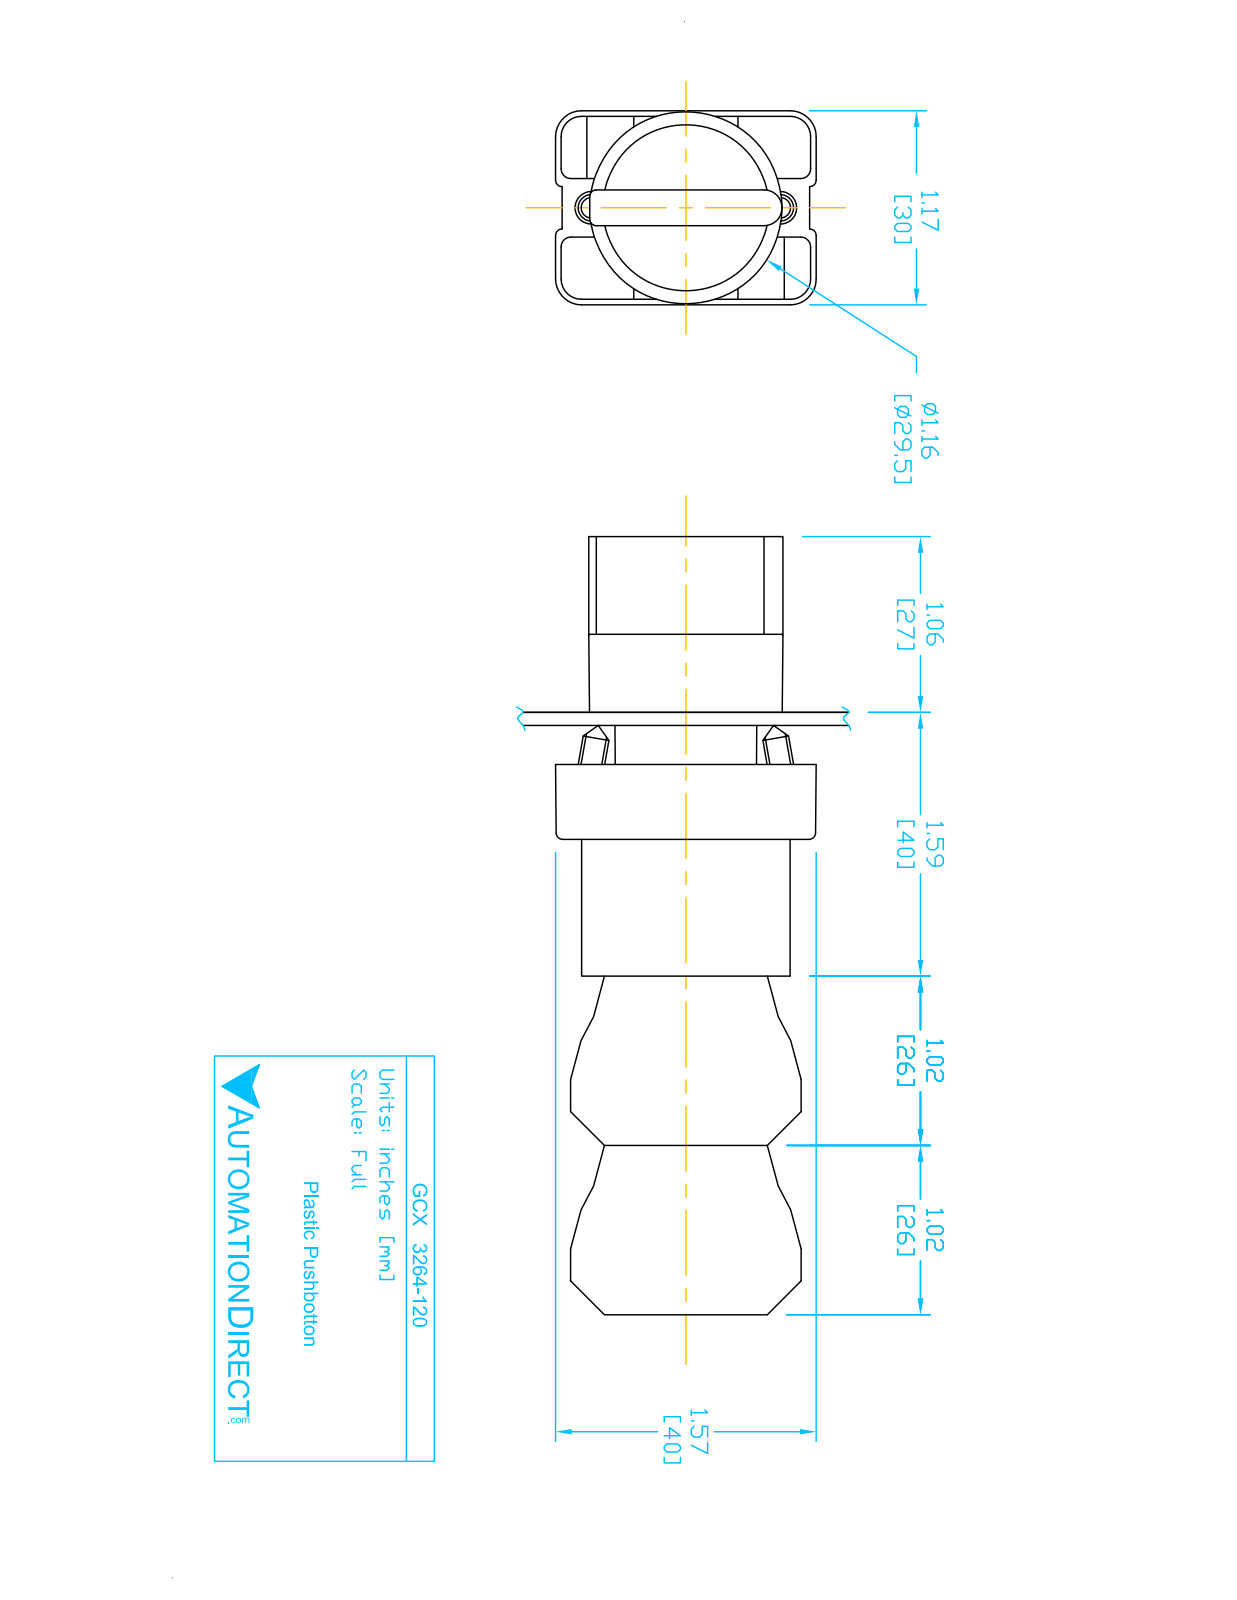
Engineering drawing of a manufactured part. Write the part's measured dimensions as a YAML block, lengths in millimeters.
part_name: "GCX3264 OPERATOR; ecx1030; ecx1040; ECX1050 (+2 more)"
step_written_by: "SolidWorks 2016 (AUTOMOTIVE_DESIGN)"
units: millimeters
bodies: {solids: 11, faces: 724, planar: 488, cylindrical: 193, other: 43}
overall_size: [118.8, 40.2, 29.9]
volume: 77850
surface_area: 38210
round_holes:
  - {diameter: 2, count: 4}
  - {diameter: 2.2, count: 2}
  - {diameter: 3.1, count: 2}
  - {diameter: 3.3, count: 2}
  - {diameter: 5, count: 1}
  - {diameter: 11.9, count: 1}
  - {diameter: 22.3, count: 1}
  - {diameter: 22.6, count: 1}
  - {diameter: 26, count: 1}
round_bosses_or_shafts:
  - {diameter: 4, count: 4}
  - {diameter: 29.8, count: 1}
  - {diameter: 25.5, count: 1}
  - {diameter: 24, count: 1}
  - {diameter: 21.7, count: 1}
  - {diameter: 19.8, count: 1}
  - {diameter: 12.8, count: 1}
partial_cylinders:
  - {radius: 1.5, count: 24}
  - {radius: 1, count: 12}
  - {radius: 3.1, count: 12}
  - {radius: 4, count: 12}
  - {radius: 1, count: 9}
  - {radius: 0.5, count: 2}
  - {radius: 1.6, count: 2}
  - {radius: 2, count: 2}
face_to_face_distances: [14.7, 15.1, 26, 29.7, 0.4, 21, 47, 77.3, 51.3, 30.3]
hole_center_spacings: [6, 25.5, 24.7, 12, 13.7, 13.8, 27.5, 12.3]
